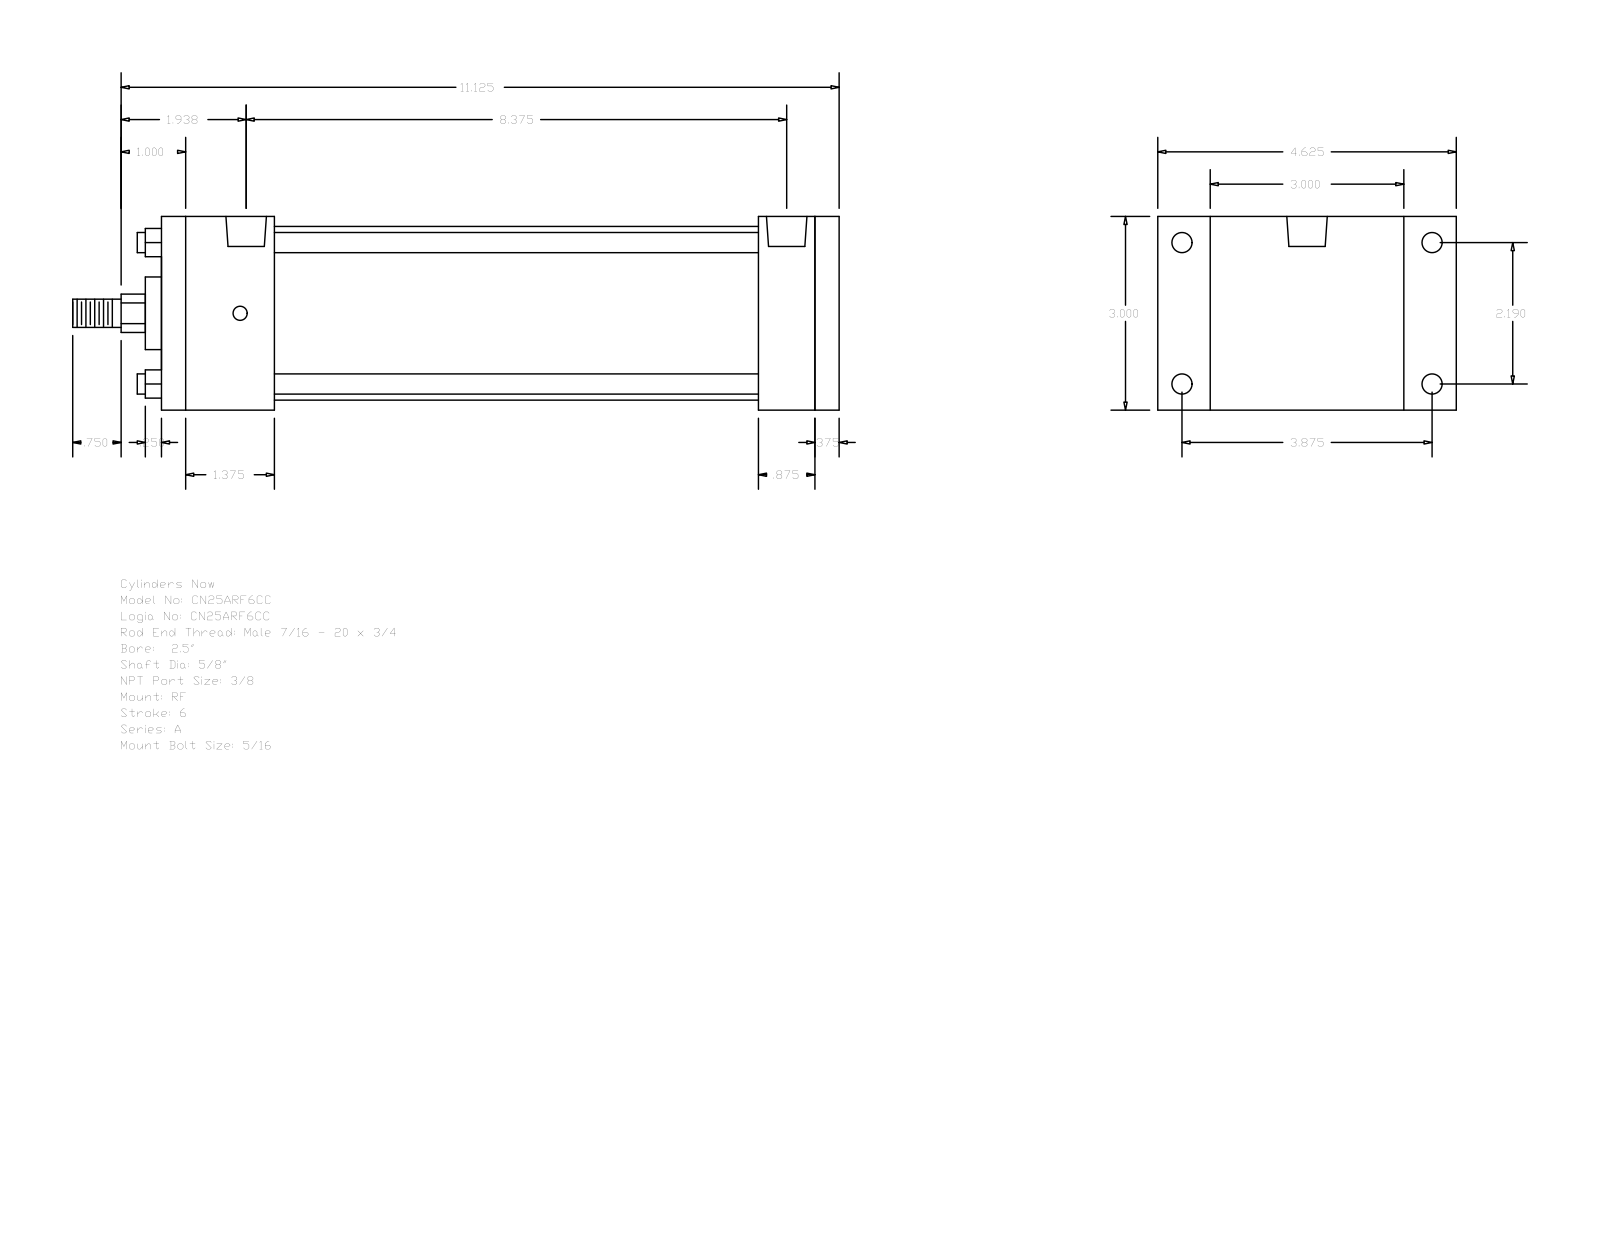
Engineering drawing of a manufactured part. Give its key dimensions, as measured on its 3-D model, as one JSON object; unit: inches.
{"part_name": "A_RF__0250_0.625", "step_written_by": "GSSL Pune (CONFIG_CONTROL_DESIGN)", "units": "inches", "bodies": {"solids": 0, "faces": 92, "planar": 64, "cylindrical": 28, "other": 0}, "overall_size": [11.875, 4.625, 3], "round_holes": [[0.219, 4], [0.313, 4], [0.627, 2]], "round_bosses_or_shafts": [[0.313, 4], [2.69, 1], [1.125, 1], [0.625, 1], [0.437, 1]], "partial_cylinders_radius": [[0.297, 1]], "face_to_face_distances": [3, 10.5, 10.125, 0.375, 1.75, 1.25, 9.25, 7.5, 8.375, 8.75], "hole_center_spacings": [0.094, 2.19, 3.875, 4.451, 8.469, 8.563, 8.375]}
